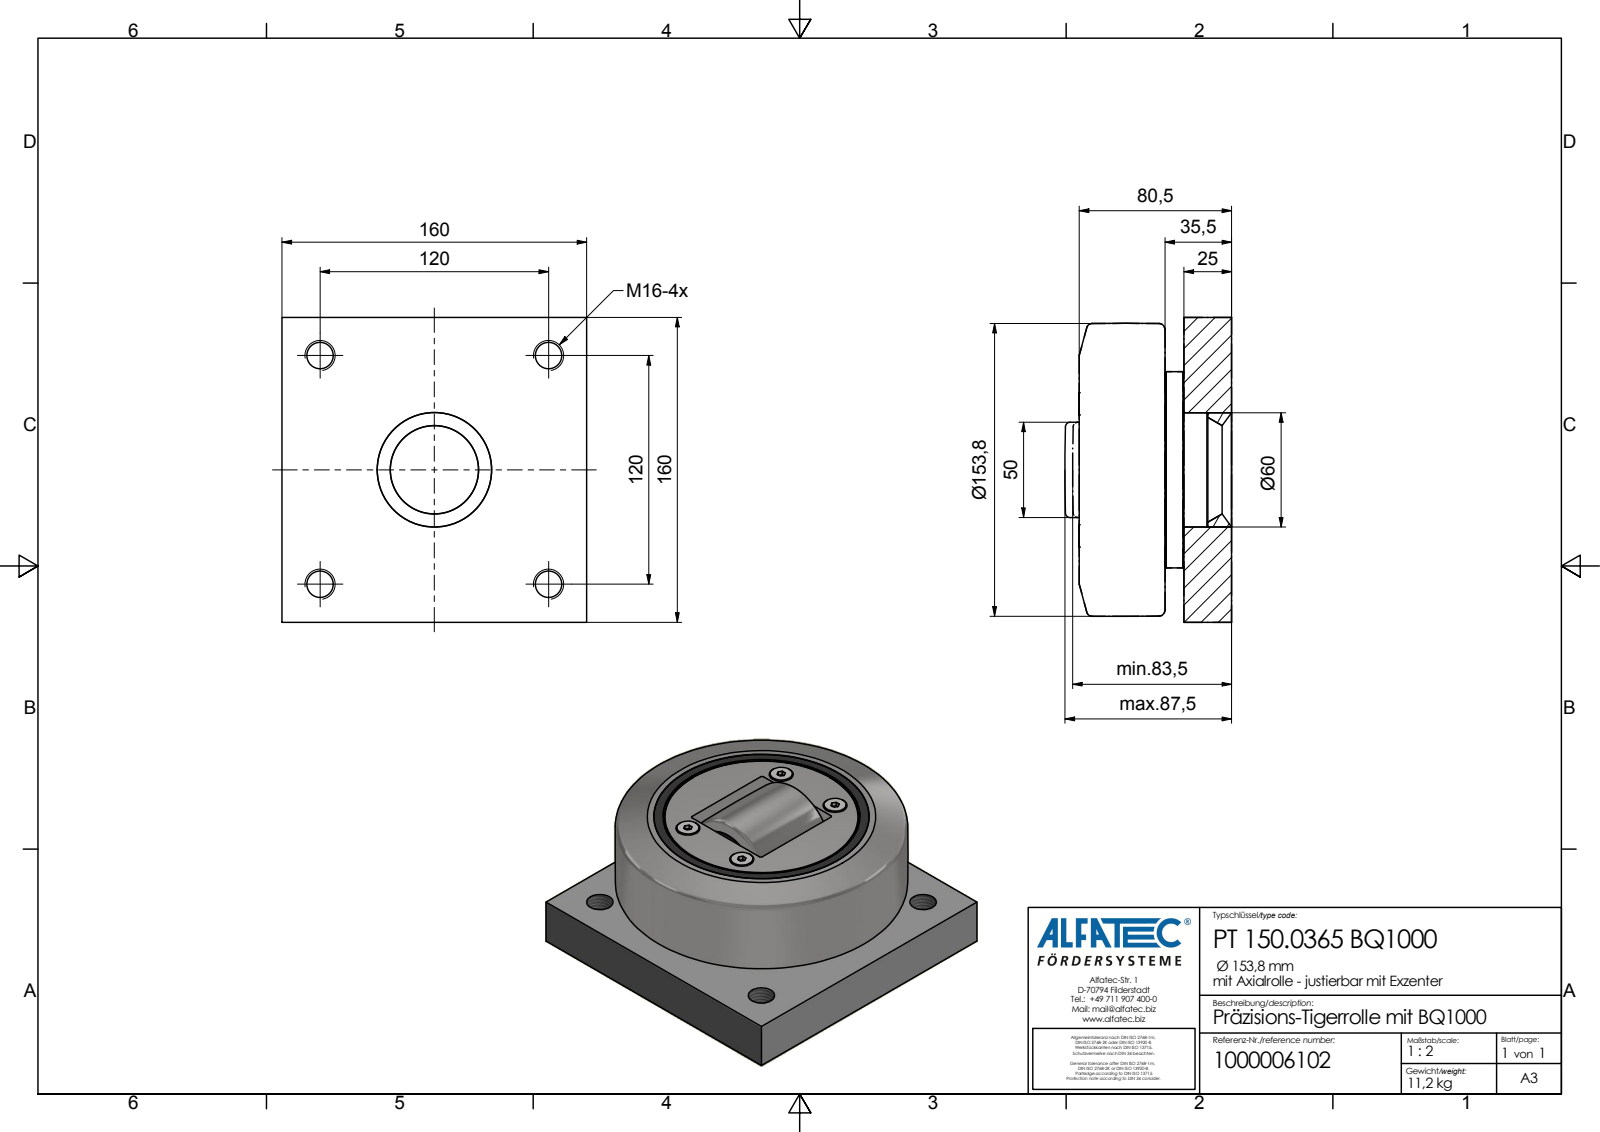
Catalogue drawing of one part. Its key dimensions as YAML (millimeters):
part_name: "PT 150.0365 BQ1000_Kontur"
step_written_by: "Autodesk Inventor 2020 (AP242_MANAGED_MODEL_BASED_3D_ENGINEERING_MIM_LF)"
units: millimeters
bodies: {solids: 1, faces: 70, planar: 47, cylindrical: 14, other: 9}
overall_size: [160, 160, 87.49]
volume: 1534000
surface_area: 114237
round_holes:
  - {diameter: 13.84, count: 4}
round_bosses_or_shafts:
  - {diameter: 11.7, count: 4}
  - {diameter: 103, count: 1}
  - {diameter: 101.4, count: 1}
partial_cylinders:
  - {radius: 20.4, count: 1}
  - {radius: 20.5, count: 1}
face_to_face_distances: [25, 55, 80, 35, 10, 45, 160, 80.22, 55.22, 45.22]
hole_center_spacings: [120, 169.71]
